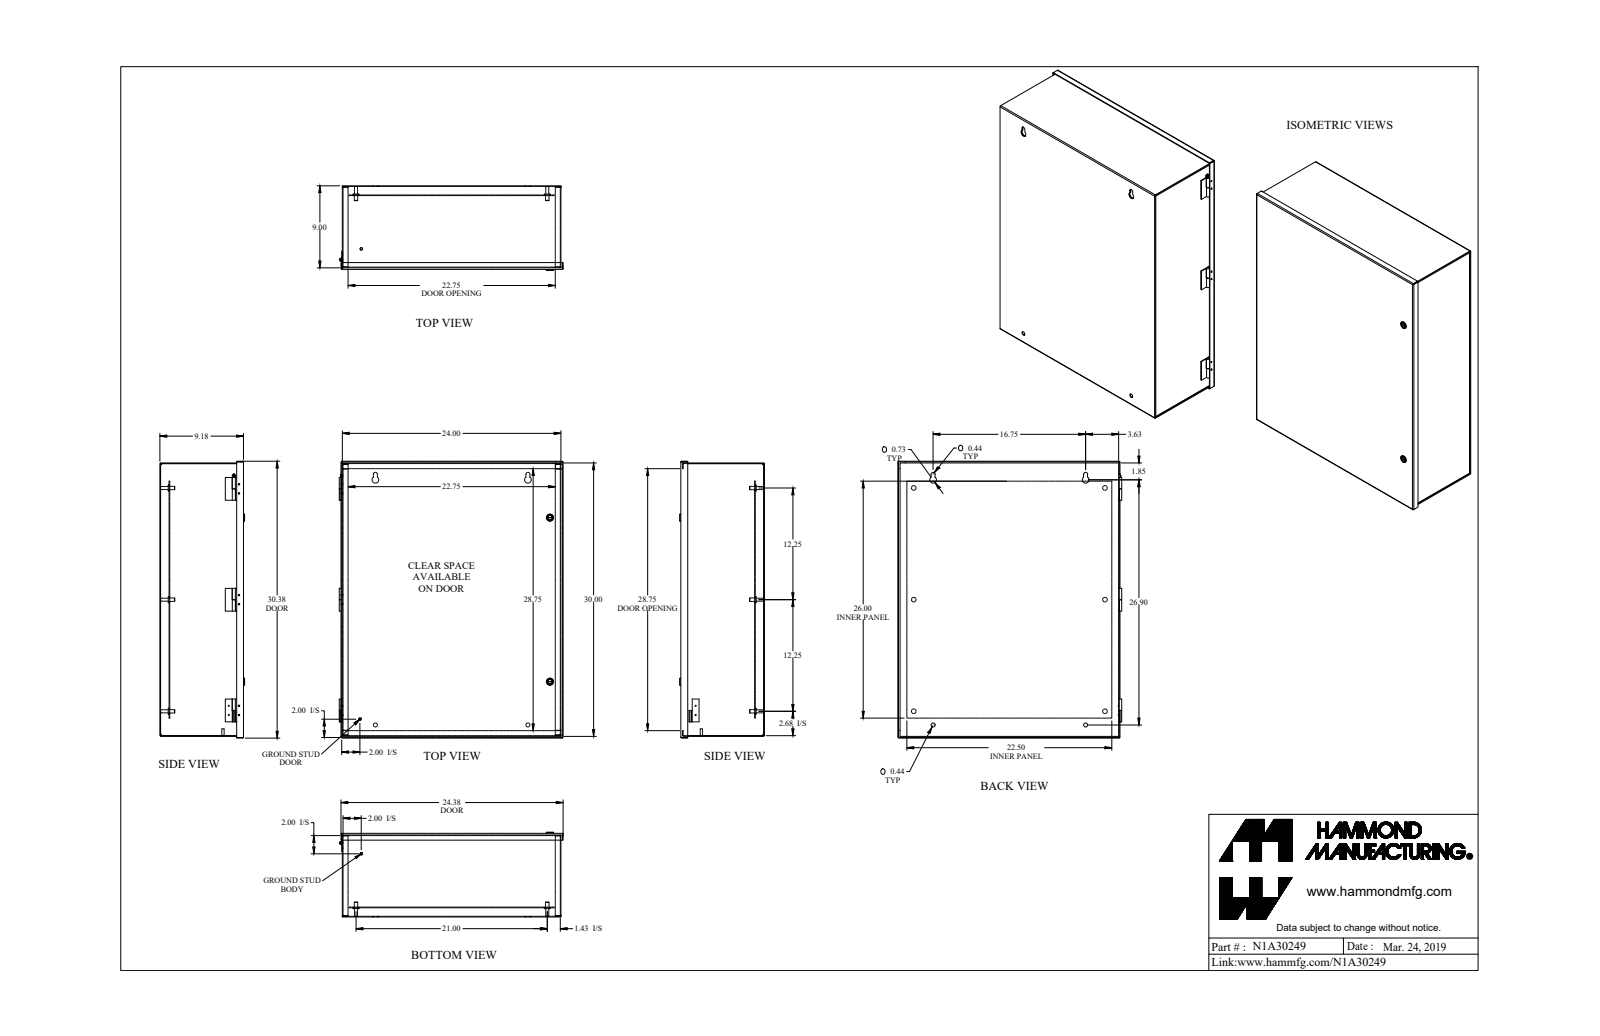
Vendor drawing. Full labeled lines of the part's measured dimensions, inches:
Part name (STEP PRODUCT): N1A30249
STEP written by: SolidWorks 2018 (AUTOMOTIVE_DESIGN)
Units: inches
Bodies: 34 solids, 767 faces (434 planar, 269 cylindrical, 64 other)
Overall size (bounding box): 30.384 × 24.574 × 9.299
Volume: 233.3 in³ · Surface area: 6 493 in²
Round holes (diameter × count): ⌀0.14 ×12, ⌀0.5 ×6, ⌀0.307 ×4, ⌀0.445 ×4, ⌀0.437 ×2, ⌀0.516 ×2, ⌀0.734 ×2, ⌀0.17 ×1, ⌀0.187 ×1
Round bosses / shafts (diameter × count): ⌀0.128 ×12, ⌀0.375 ×7, ⌀0.65 ×6, ⌀0.33 ×6, ⌀1 ×4, ⌀0.788 ×2, ⌀0.535 ×2, ⌀0.496 ×2
Partial cylindrical surfaces — rounded edges, fillets, slot ends (radius × count): R0.036 ×16, R0.108 ×16, R0.06 ×2, R0.125 ×2, R0.153 ×2, R0.219 ×2, R0.315 ×2, R0.03 ×1
Main face-to-face distances: 0.072, 9.105, 1.009, 8.096, 9.033, 9.177, 0.937, 1.081, 8.024, 8.168
Hole centre spacings: 1, 1.119, 24.312, 12.156, 12.157, 12.25, 21, 3.263
